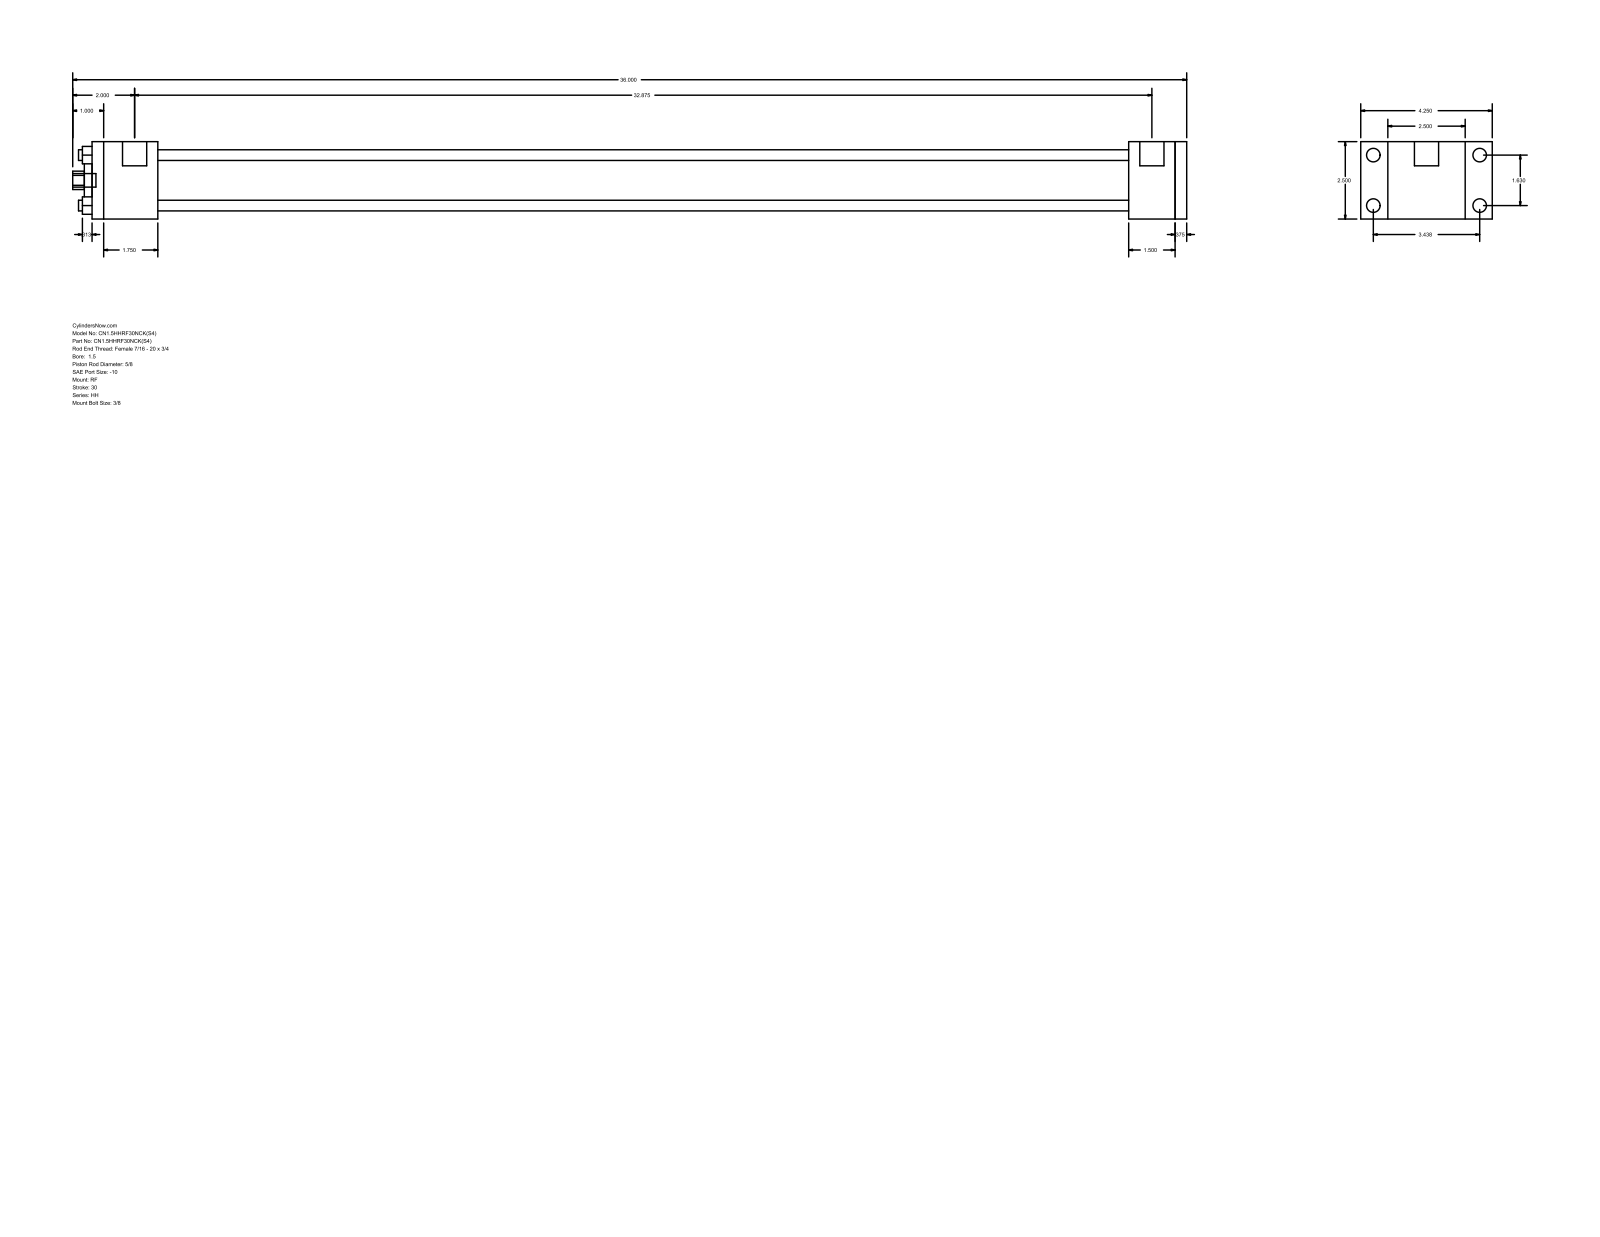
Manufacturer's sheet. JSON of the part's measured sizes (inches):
{"part_name": "HH_RF__0150_0.625", "step_written_by": "GSSL Pune (CONFIG_CONTROL_DESIGN)", "units": "inches", "bodies": {"solids": 0, "faces": 92, "planar": 64, "cylindrical": 28, "other": 0}, "overall_size": [36, 4.25, 2.5], "round_holes": [[0.345, 4], [0.625, 1], [1.125, 1], [1.75, 1]], "round_bosses_or_shafts": [[0.438, 4], [0.219, 4], [0.781, 2], [0.437, 1]], "partial_cylinders_radius": [[0.297, 1]], "face_to_face_distances": [2.5, 35.375, 0.375, 35, 1.875, 2.125, 33.5, 31.375, 32.875, 33.25], "hole_center_spacings": [1.152, 1.63, 2.305]}
